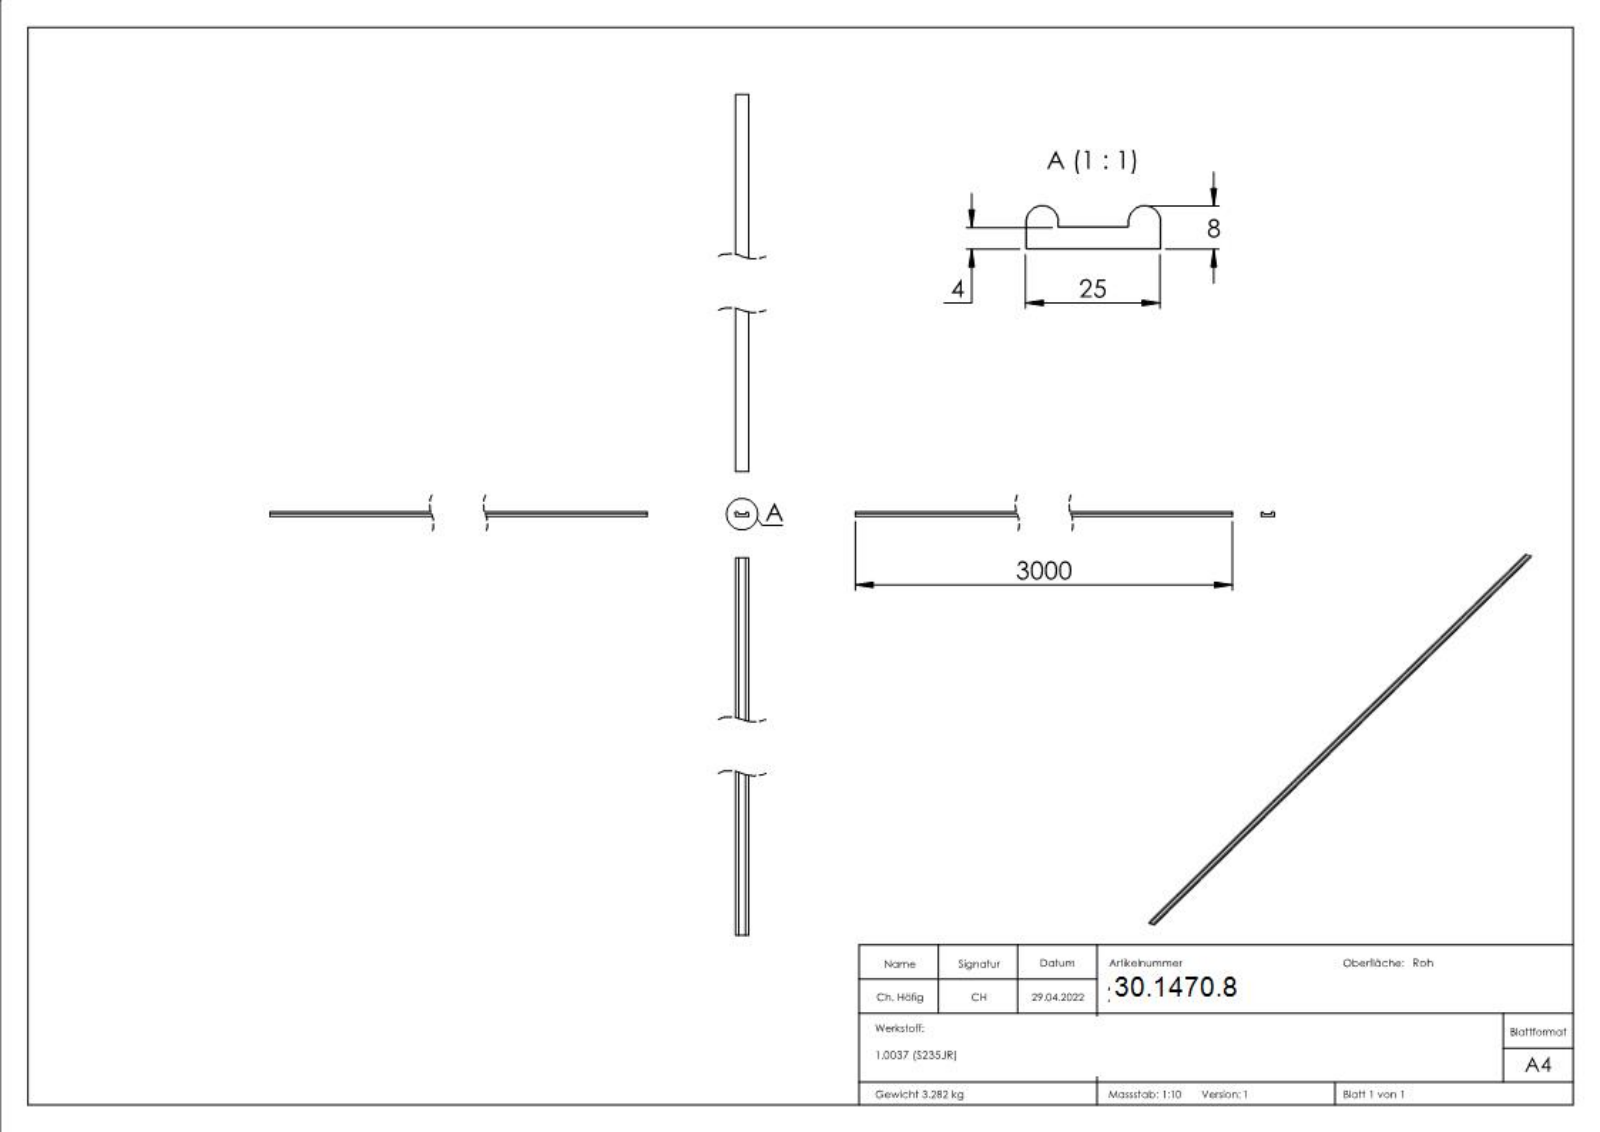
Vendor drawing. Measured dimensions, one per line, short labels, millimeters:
name: 2301
written by: SolidWorks 2018 (CONFIG_CONTROL_DESIGN)
unit: mm
bodies: 1 solid, 215 faces (116 planar, 2 cylindrical, 97 other)
size: 3000 × 25 × 8
volume: 420 822 mm³; area: 206 839 mm²
rounds: 2× R3
face distances: 4, 25, 6, 19, 13, 3000, 3.9, 7.75, 2.48, 5.25
